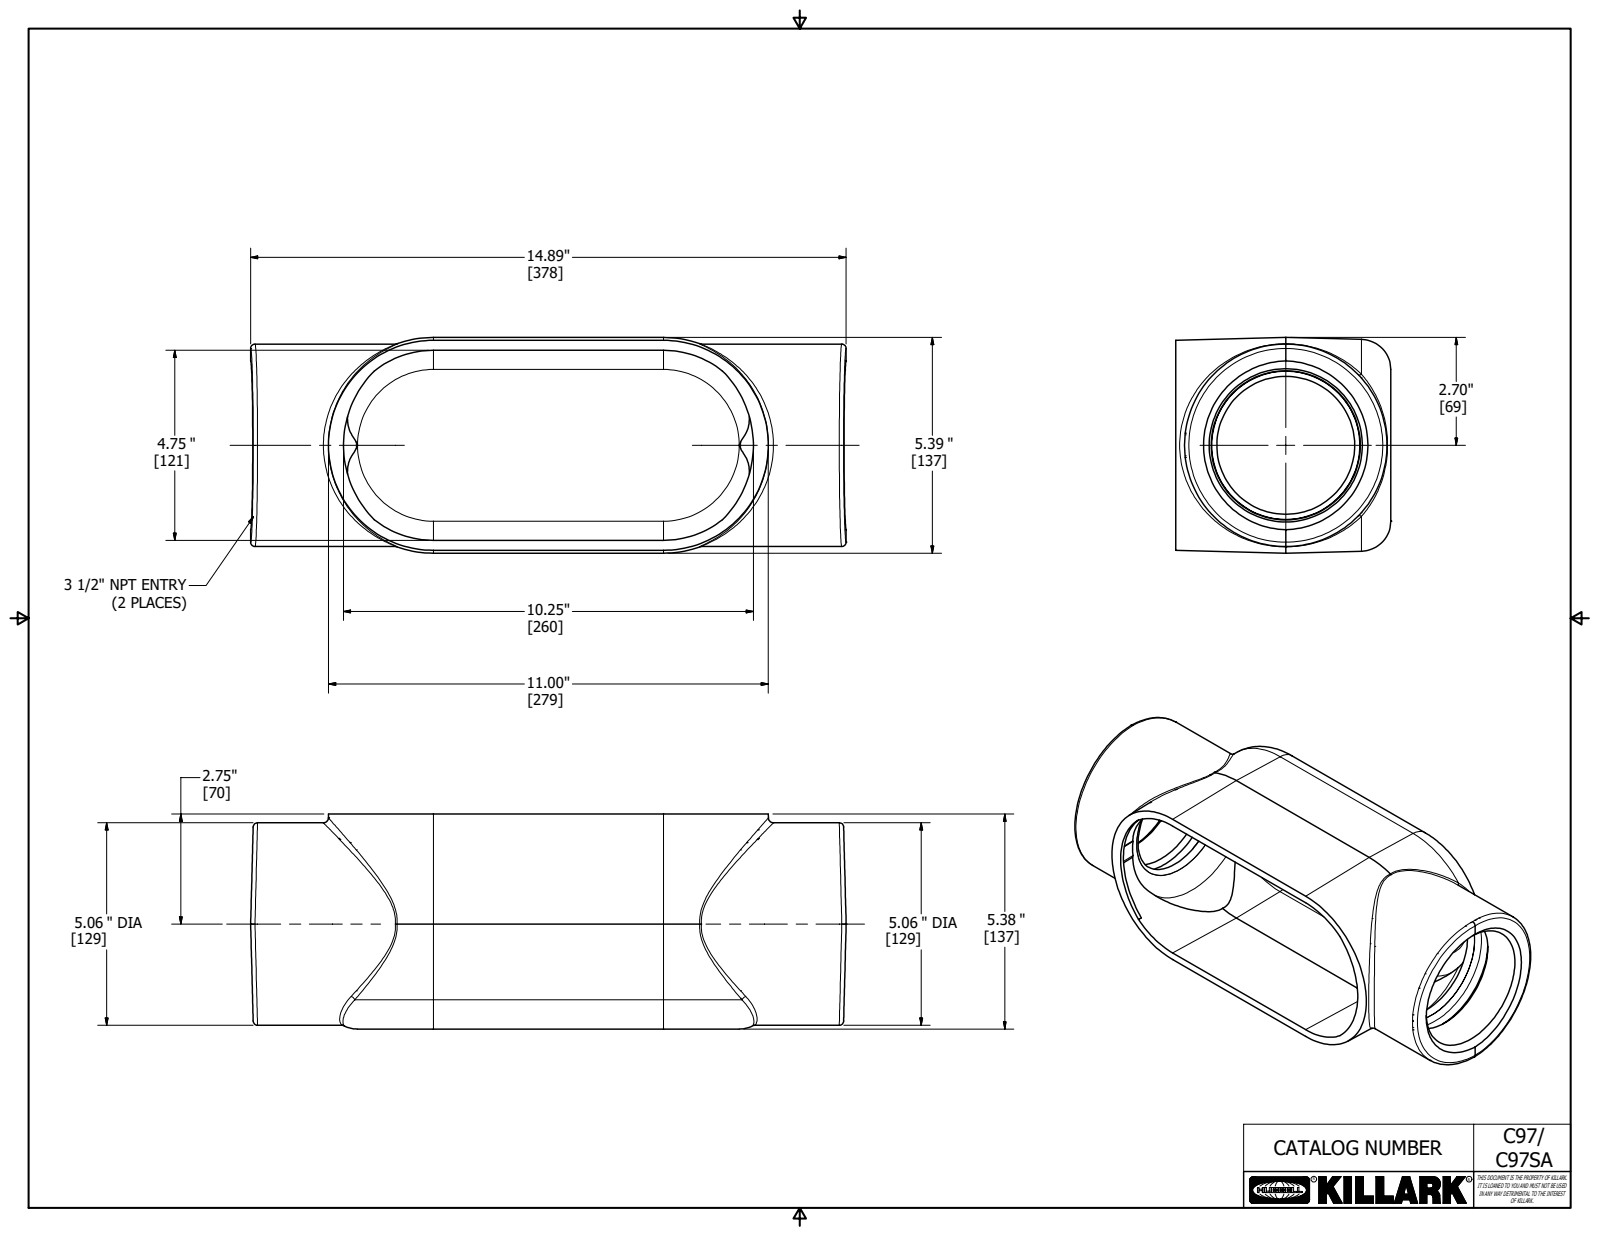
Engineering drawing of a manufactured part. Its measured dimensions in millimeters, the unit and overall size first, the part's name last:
Units: millimetres
Overall size (bounding box): 378.3 × 137 × 136.5
Round holes (diameter × count): ⌀101.9 ×1
Round bosses / shafts (diameter × count): ⌀128.6 ×1
Partial cylindrical surfaces — rounded edges, fillets, slot ends (radius × count): R1.3 ×4, R3.2 ×4, R12.7 ×2, R19.1 ×2, R60.3 ×1
Main face-to-face distances: 6.4, 130.7, 137, 124.3, 136.5, 130.2, 378.3, 0.8, 5.6, 135.7
Volume: 1 250 000 mm³ · Surface area: 307 900 mm²
Bodies: 1 solid, 96 faces (28 planar, 22 cylindrical, 46 other)
Part name (STEP PRODUCT): 17736
STEP written by: Autodesk Inventor 2018 (AUTOMOTIVE_DESIGN)
